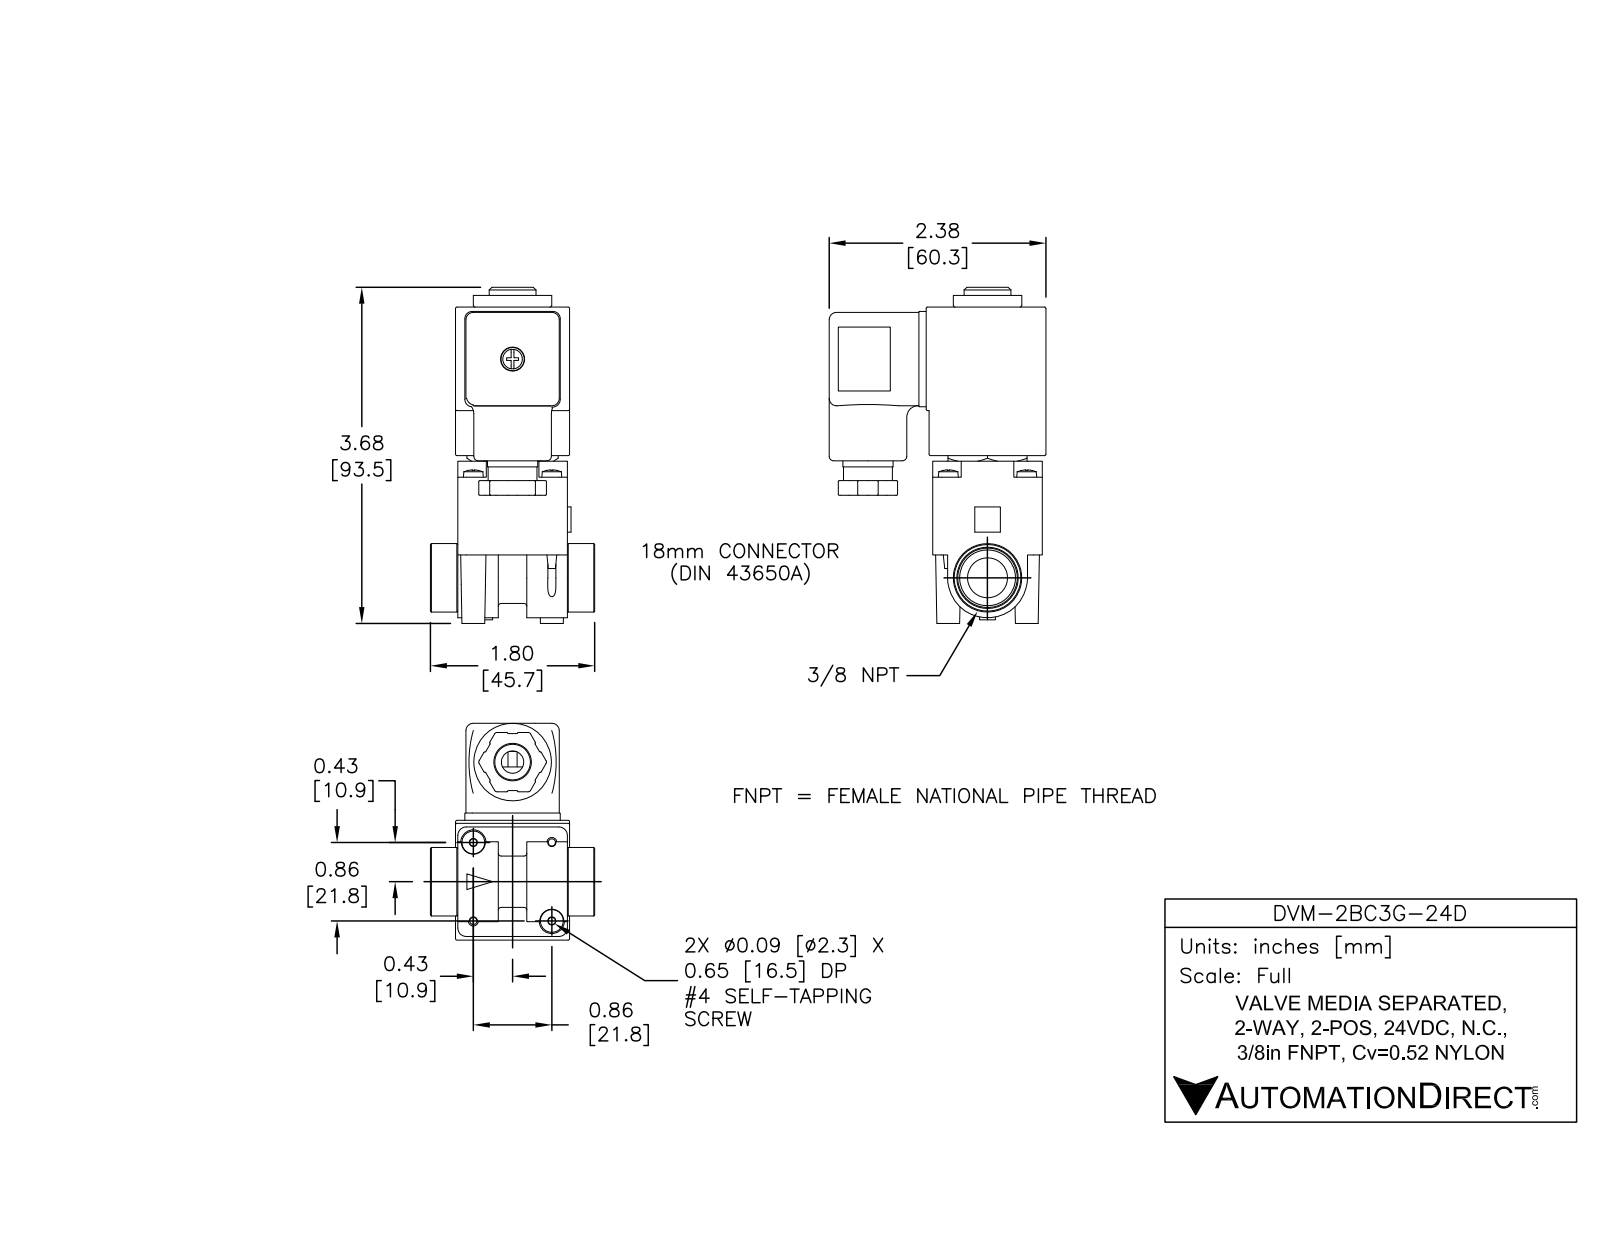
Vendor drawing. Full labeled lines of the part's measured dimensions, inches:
Part name (STEP PRODUCT): DVM-2BC3G-24D
STEP written by: SolidWorks 2015 (AUTOMOTIVE_DESIGN)
Units: inches
Bodies: 14 solids, 1775 faces (895 planar, 351 cylindrical, 529 other)
Overall size (bounding box): 3.683 × 2.375 × 1.8
Volume: 5.115 in³ · Surface area: 68.03 in²
Round holes (diameter × count): ⌀0.112 ×4, ⌀0.06 ×2, ⌀0.089 ×2, ⌀0.315 ×2, ⌀0.12 ×1, ⌀0.157 ×1, ⌀0.203 ×1, ⌀0.245 ×1, ⌀0.25 ×1, ⌀0.263 ×1, ⌀0.39 ×1, ⌀0.4 ×1
Round bosses / shafts (diameter × count): ⌀0.217 ×4, ⌀0.125 ×4, ⌀0.875 ×1, ⌀0.875 ×1, ⌀0.85 ×1, ⌀0.807 ×1, ⌀0.68 ×1, ⌀0.535 ×1
Partial cylindrical surfaces — rounded edges, fillets, slot ends (radius × count): R0.01 ×54, R0.005 ×21, R0.016 ×17, R0.02 ×12, R0.03 ×12, R0.031 ×12, R0.08 ×12, R0.05 ×8
Main face-to-face distances: 1.25, 1.2, 0.163, 1.087, 0.048, 0.137, 0.974, 1.225, 0.963, 0.04
Hole centre spacings: 0.608, 0.608, 0.684, 0.86, 0.86, 0.98, 1.216, 1.457
